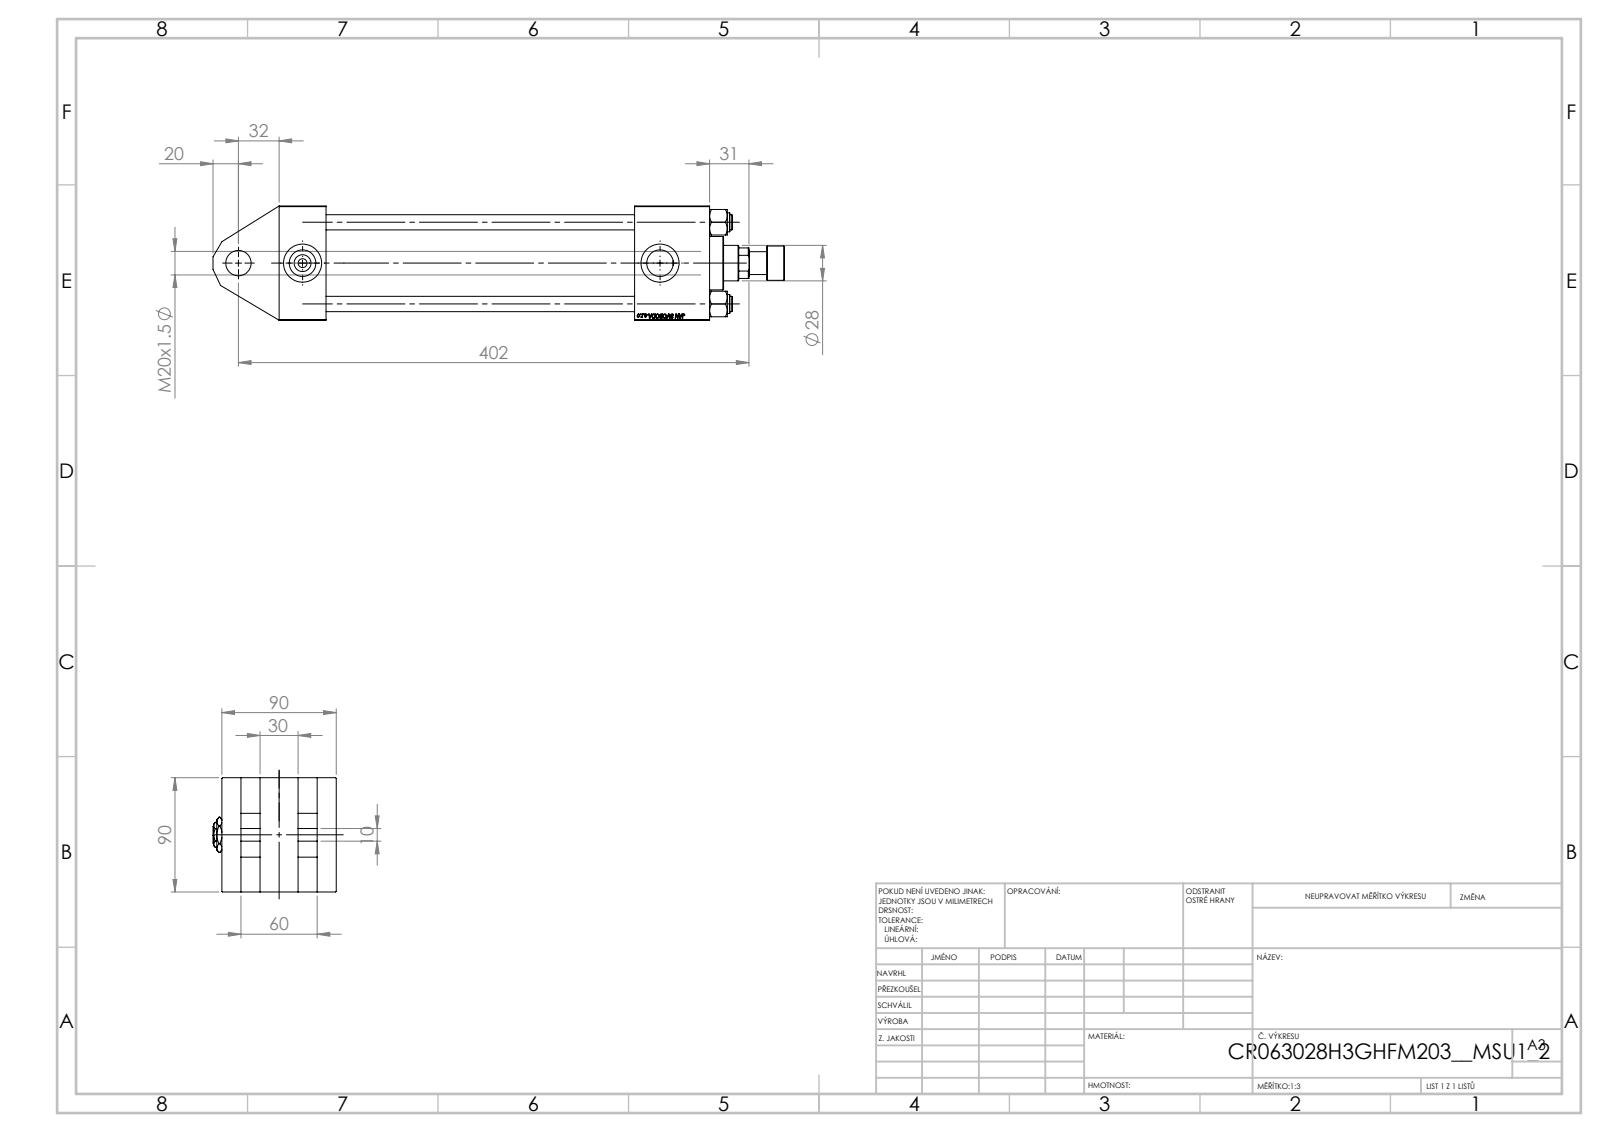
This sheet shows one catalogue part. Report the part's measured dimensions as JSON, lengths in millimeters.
{"part_name": "Zatka_pro_OIL_PORT; V215CR_TYCINKA_H; V215CR_VCP_H; V215CR_ROD_END_F (+3 more)", "step_written_by": "SolidWorks 2019 (CONFIG_CONTROL_DESIGN)", "units": "millimeters", "bodies": {"solids": 14, "faces": 1244, "planar": 570, "cylindrical": 98, "other": 576}, "overall_size": [450, 97, 90], "volume_mm3": 1354000, "surface_area_mm2": 324800, "round_holes": [[12, 4], [7, 2], [20.96, 2], [30, 2], [18.5, 1], [20, 1], [28, 1], [31, 1], [50, 1], [60, 1], [63, 1]], "round_bosses_or_shafts": [[15, 4], [69, 1], [42, 1], [27, 1], [18, 1]], "face_to_face_distances": [90, 15, 60, 30, 302, 45, 37, 59, 75, 339], "hole_center_spacings": [45.47, 64.3, 90.93, 50.5, 281.5, 332]}
